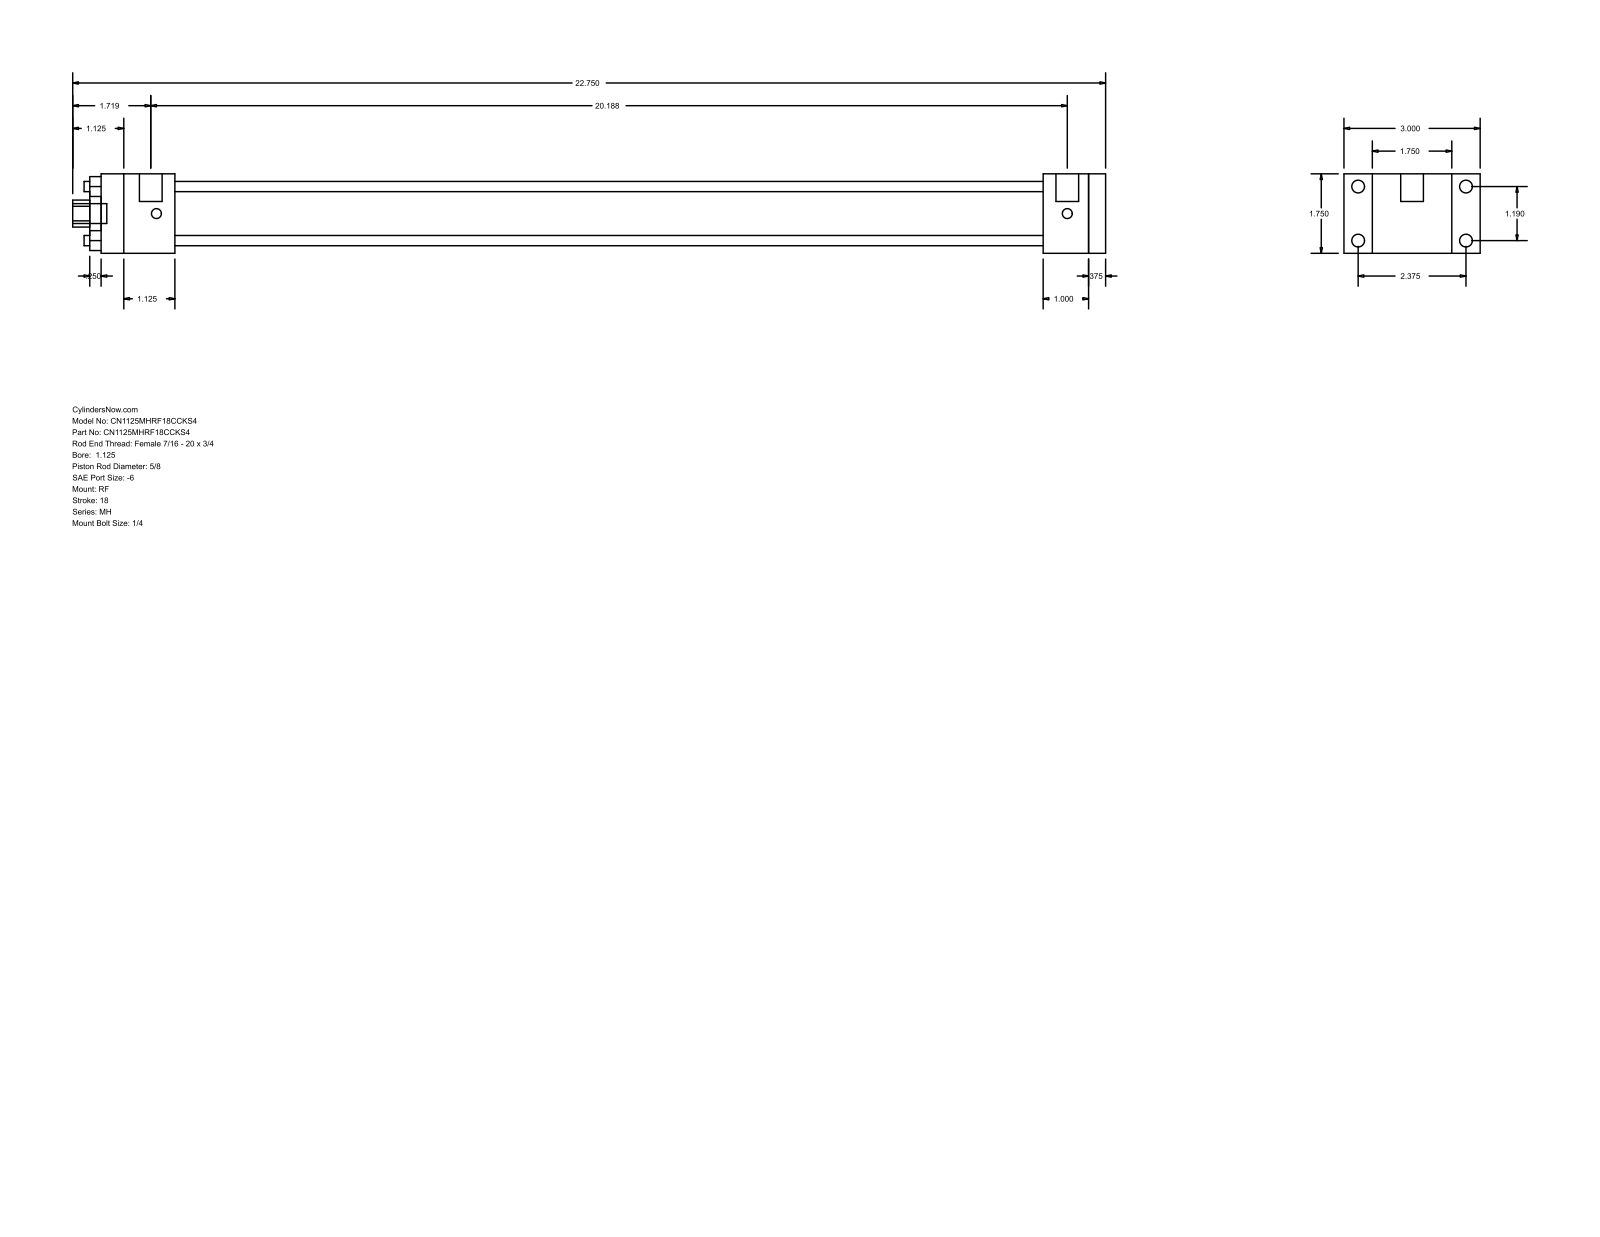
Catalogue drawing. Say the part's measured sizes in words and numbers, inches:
The part is named "MH_RF__0112_0.625". Its 3-D file was written by "GSSL Pune (CONFIG_CONTROL_DESIGN)". It is 0 solids with 92 faces: 64 planar, 28 cylindrical and 0 other. Overall it measures 22.75 by 3 by 1.75 inches. Round holes: 4 of diameter 0.225, 1 of diameter 0.625, 1 of diameter 1.125, 1 of diameter 1.375. Round bosses or shafts: 4 of diameter 0.281, 4 of diameter 0.219, 2 of diameter 0.5, 1 of diameter 0.437. Partial cylindrical surfaces (rounded edges, fillets, slot ends): 1 of radius 0.297. The main face-to-face distances are 1.75, 0.375, 0.625, 20.125, 20.5, 19.125, 1, 1.375, 1.625, 20.75. The hole center spacings are 0.841, 1.19, 1.683.
